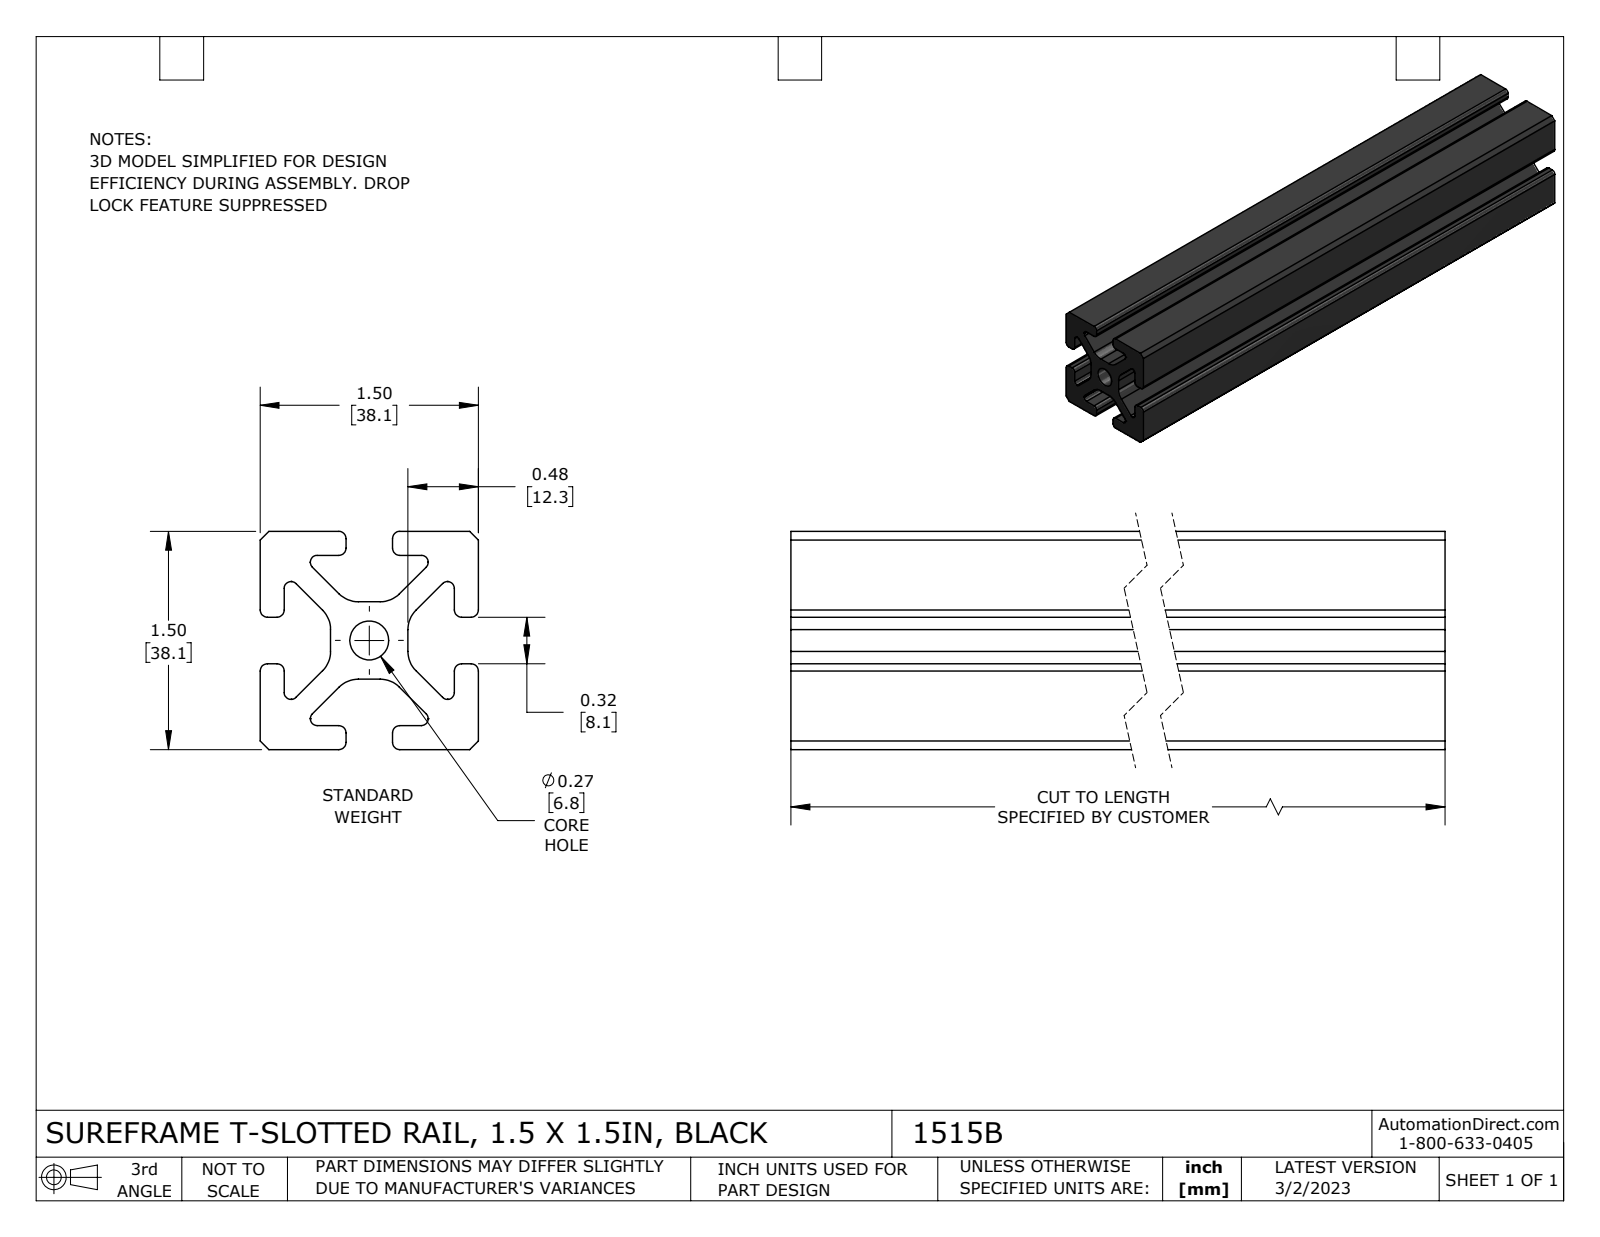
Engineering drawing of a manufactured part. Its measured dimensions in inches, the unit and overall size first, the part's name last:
Units: inches
Overall size (bounding box): 8 × 1.5 × 1.5
Round holes (diameter × count): ⌀0.268 ×1
Partial cylindrical surfaces — rounded edges, fillets, slot ends (radius × count): R0.047 ×16, R0.05 ×16, R0.188 ×7, R0.187 ×1
Main face-to-face distances: 1.5, 0.165, 1.335, 0.16, 0.484, 1.016, 0.319, 0.851, 1.17, 0.59
Volume: 9.582 in³ · Surface area: 104.2 in²
Bodies: 1 solid, 92 faces (50 planar, 42 cylindrical, 0 other)
Part name (STEP PRODUCT): 1515B
STEP written by: SolidWorks 2021 (CONFIG_CONTROL_DESIGN)
